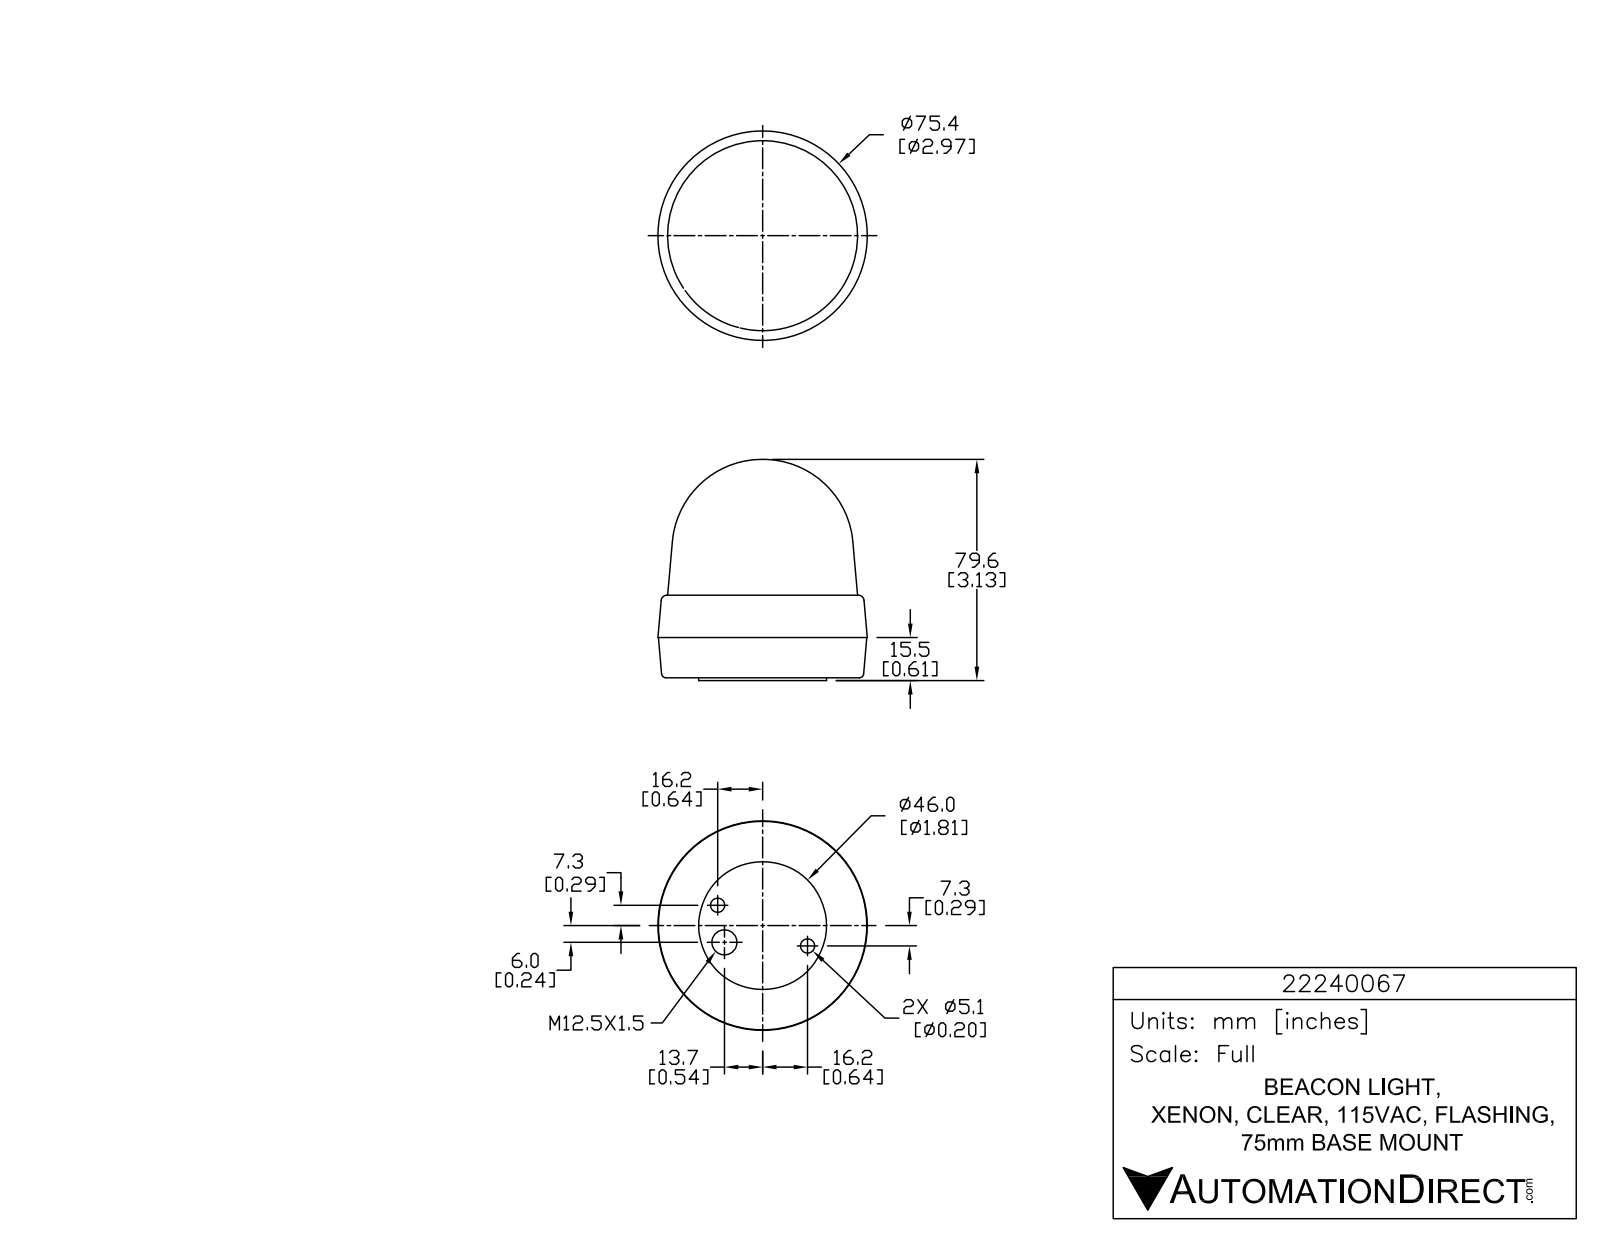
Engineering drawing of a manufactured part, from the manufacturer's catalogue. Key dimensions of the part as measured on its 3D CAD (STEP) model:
Part name (STEP PRODUCT): 22240067
STEP written by: SolidWorks 2015 (AUTOMOTIVE_DESIGN)
Units: inches
Bodies: 1 solid, 773 faces (526 planar, 163 cylindrical, 84 other)
Overall size (bounding box): 3.133 × 2.967 × 2.967
Volume: 15.79 in³ · Surface area: 33.7 in²
Round holes (diameter × count): ⌀0.059 ×3, ⌀0.201 ×2, ⌀0.354 ×1
Round bosses / shafts (diameter × count): ⌀0.339 ×3, ⌀0.084 ×3, ⌀1.811 ×1
Partial cylindrical surfaces — rounded edges, fillets, slot ends (radius × count): R0.005 ×9, R0.005 ×6, R0.012 ×6, R0.012 ×6, R0.012 ×6, R0.196 ×6, R0.005 ×3, R0.005 ×3
Main face-to-face distances: 0.039, 1.209, 1.17, 0.61, 0.571, 0.599, 1.566, 1.527, 0.956, 0.357
Hole centre spacings: 0.534, 1.179, 1.398
